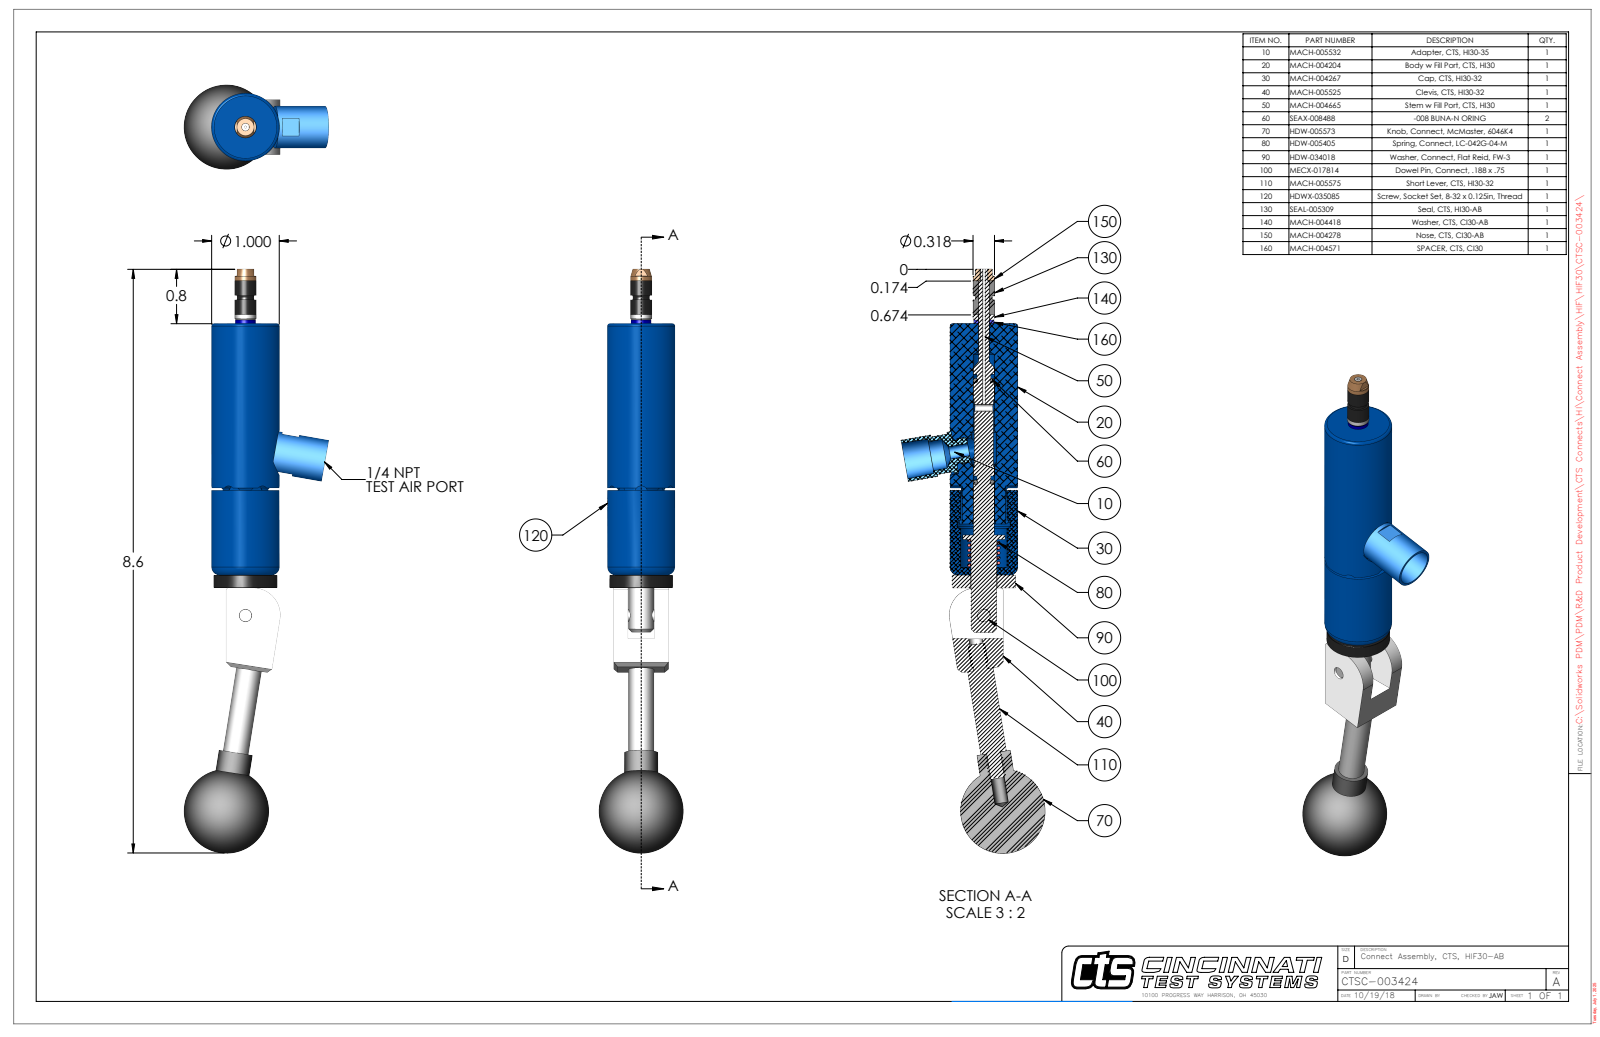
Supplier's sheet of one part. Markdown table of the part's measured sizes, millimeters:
| quantity | value |
| --- | --- |
| part name | CTSC-003424 |
| STEP written by | SolidWorks 2023 (AUTOMOTIVE_DESIGN) |
| units | millimeters |
| bodies | 11 solids, 280 faces (96 planar, 122 cylindrical, 62 other) |
| overall size | 219.2 × 54.1 × 31.8 |
| volume | 80 760 mm³ |
| surface area | 23 610 mm² |
| round holes (diameter × count) | 5.1 × 2, 1 × 1, 2.1 × 1, 2.9 × 1, 3.5 × 1, 3.8 × 1, 3.9 × 1, 4.1 × 1, 4.2 × 1, 4.7 × 1, 4.8 × 1, 9.8 × 1 |
| round bosses / shafts (diameter × count) | 25.4 × 1, 23.8 × 1, 15.7 × 1, 12.7 × 1, 9.7 × 1, 9.5 × 1, 8.1 × 1, 8.1 × 1 |
| partial cylindrical surfaces (radius × count) | 2.4 × 6, 0.4 × 1, 1.4 × 1, 8.3 × 1, 10.2 × 1, 11.9 × 1 |
| main face-to-face distances | 5.3, 15.3, 20.6, 4.7, 94.4, 99.2, 9.9, 62.6, 31.8, 36.6 |
| hole center spacings | 15.2, 42.1, 57.2 |
